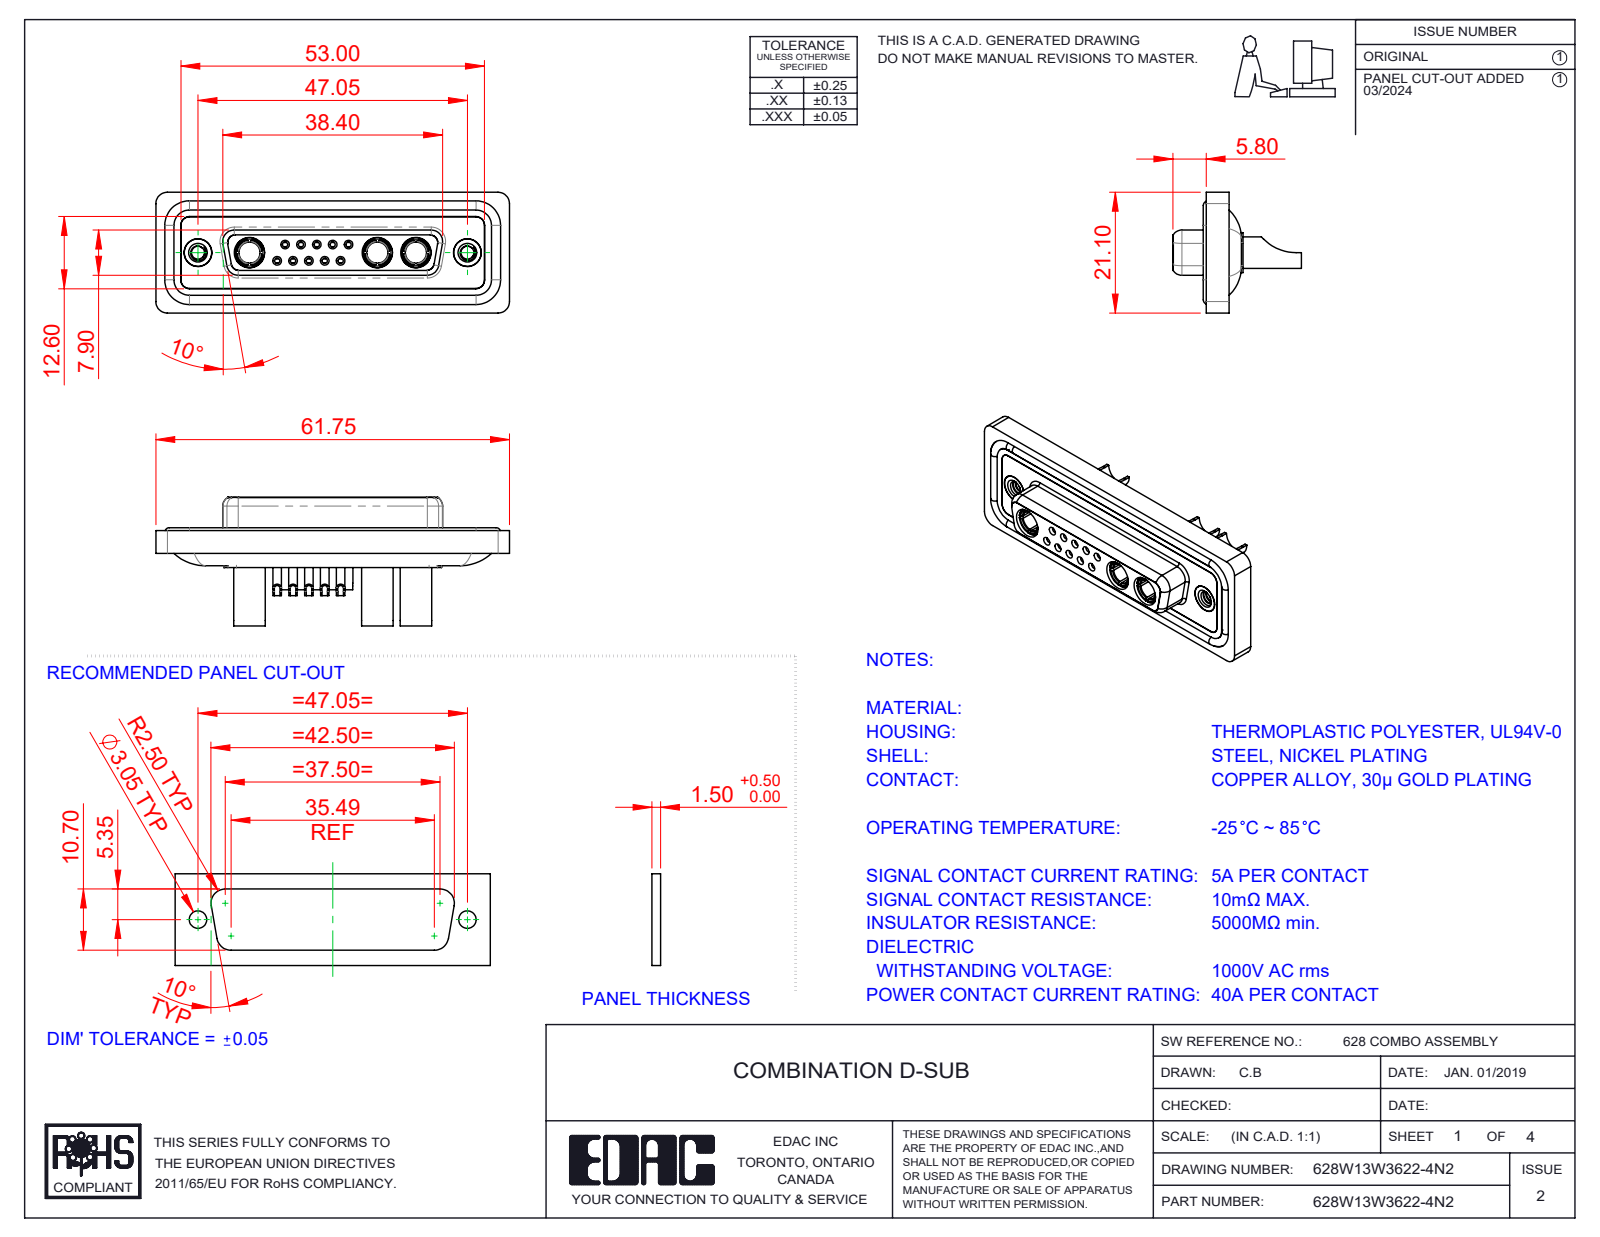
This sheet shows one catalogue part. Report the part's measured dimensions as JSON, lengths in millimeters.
{"part_name": "628Combo Waterproof Housing_25 Contacts; 628Combo Contact Row 2_22; 628Combo Shell Front_25 Contacts; 628Combo Contact Row 1_22 (+5 more)", "step_written_by": "SolidWorks 2023 (CONFIG_CONTROL_DESIGN)", "units": "millimeters", "bodies": {"solids": 23, "faces": 1167, "planar": 368, "cylindrical": 470, "other": 329}, "overall_size": [61.75, 22.45, 21.1], "volume_mm3": 8413, "surface_area_mm2": 14233, "round_holes": [[0.9, 10], [1, 10], [1.1, 10], [1.5, 10], [2, 10], [1.6, 5], [1.7, 5], [4.85, 5], [3.7, 3], [4.6, 3], [5.3, 3], [2.26, 2]], "round_bosses_or_shafts": [[2.2, 10], [1.6, 9], [5.5, 3], [5.2, 3], [4.96, 3], [4.75, 3], [3.75, 3], [4.95, 2]], "partial_cylinders_radius": [[1.5, 22], [2, 18], [1.35, 8], [1.6, 8], [1, 6], [0.25, 4], [0.5, 4], [0.6, 4]], "face_to_face_distances": [0.4, 7.45, 1.8, 5.65, 0.5, 6.6, 7.05, 1.6, 2.9, 1.1], "hole_center_spacings": [3.16, 2.77, 5.03, 5.04, 5.54, 8.31, 7.49, 2.76]}
